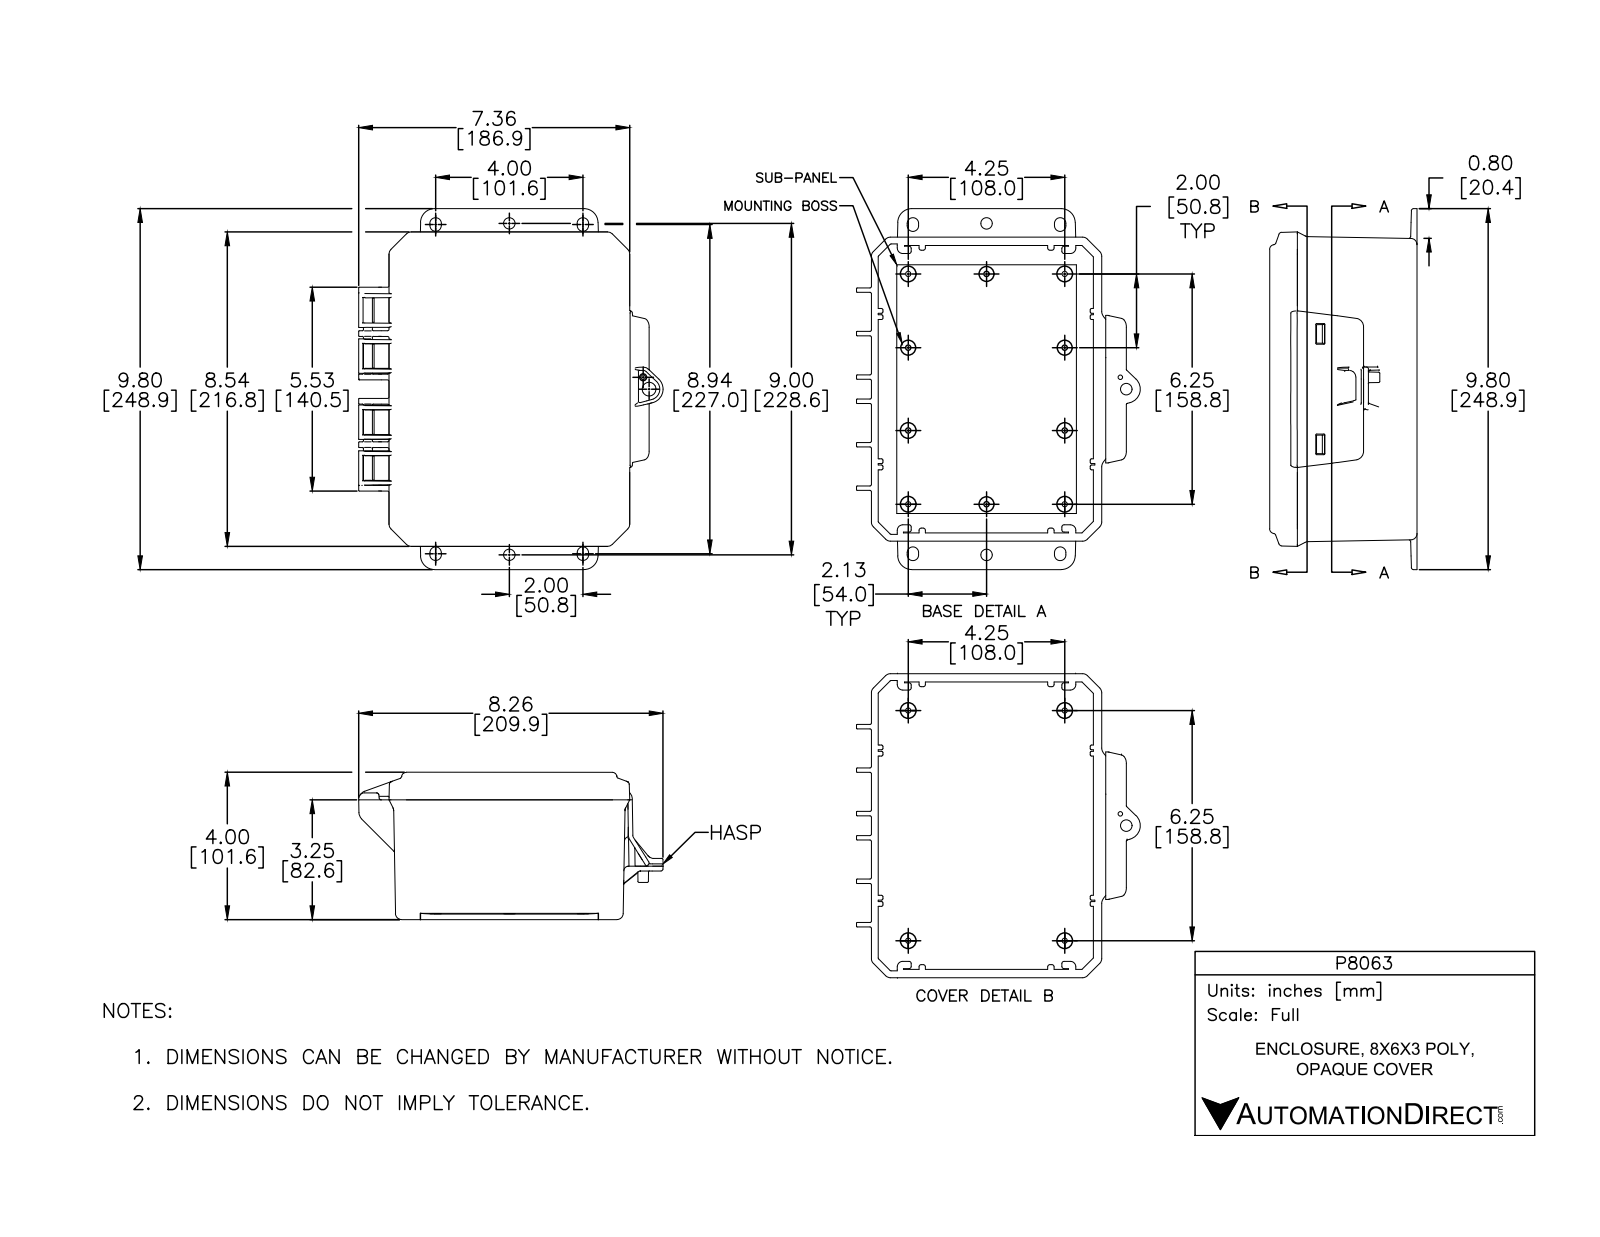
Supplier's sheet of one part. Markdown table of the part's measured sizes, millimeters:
| quantity | value |
| --- | --- |
| part name | 8X6X3-BOX-SD-HINGE-INT-LATCH_12; P8063; 8X6-LID-SD-HINGE-INT-LATCH_126 |
| STEP written by | SolidWorks 2016 (AUTOMOTIVE_DESIGN) |
| units | millimeters |
| bodies | 1 solid, 2304 faces (575 planar, 849 cylindrical, 880 other) |
| overall size | 248.9 × 210 × 101.7 |
| volume | 217 900 mm³ |
| surface area | 341 500 mm² |
| round holes (diameter × count) | 3.6 × 10, 3 × 1 |
| round bosses / shafts (diameter × count) | 6.1 × 1 |
| partial cylindrical surfaces (radius × count) | 0.5 × 124, 0.8 × 117, 0.4 × 63, 1 × 54, 0.3 × 33, 1.5 × 32, 4.8 × 17, 1.3 × 15 |
| main face-to-face distances | 3.8, 12, 9.5, 82.6, 78.7, 161.6, 157.8, 2.5, 3, 145.1 |
| hole center spacings | 50.8, 54, 74.1, 108, 108, 119.3, 120.7, 152.7 |
